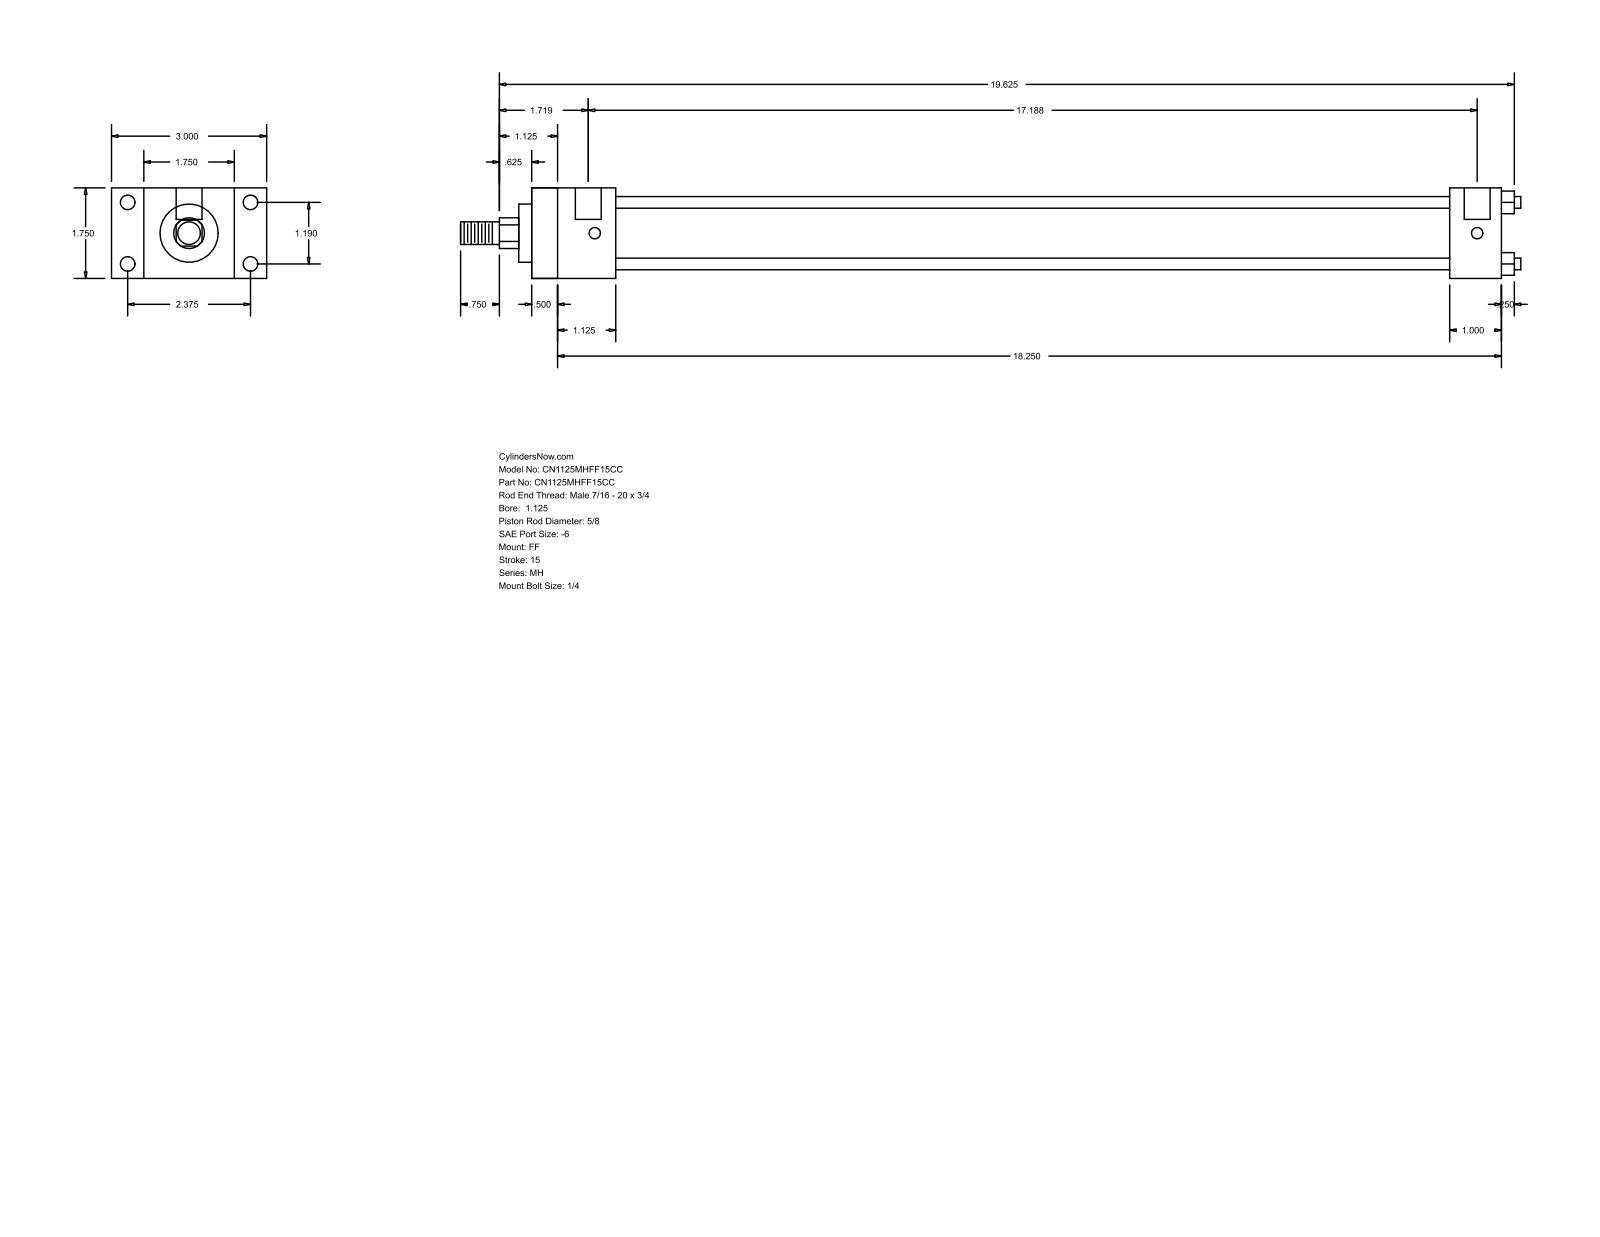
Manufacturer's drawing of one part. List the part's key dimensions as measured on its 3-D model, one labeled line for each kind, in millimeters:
Part name (STEP PRODUCT): MH_FF__0112_0.625
STEP written by: GSSL Pune (CONFIG_CONTROL_DESIGN)
Units: millimetres
Bodies: 0 solids, 92 faces (64 planar, 28 cylindrical, 0 other)
Overall size (bounding box): 520.7 × 76.2 × 44.45
Round holes (diameter × count): ⌀5.56 ×4, ⌀7.14 ×4, ⌀12.7 ×2
Round bosses / shafts (diameter × count): ⌀5.71 ×4, ⌀34.92 ×1, ⌀28.57 ×1, ⌀15.88 ×1, ⌀11.11 ×1
Partial cylindrical surfaces — rounded edges, fillets, slot ends (radius × count): R7.54 ×1
Main face-to-face distances: 44.46, 476.24, 12.69, 463.55, 15.87, 28.58, 60.33, 41.27, 450.85, 438.16
Hole centre spacings: 30.22, 60.32, 67.47, 433.39, 3.17, 436.56
